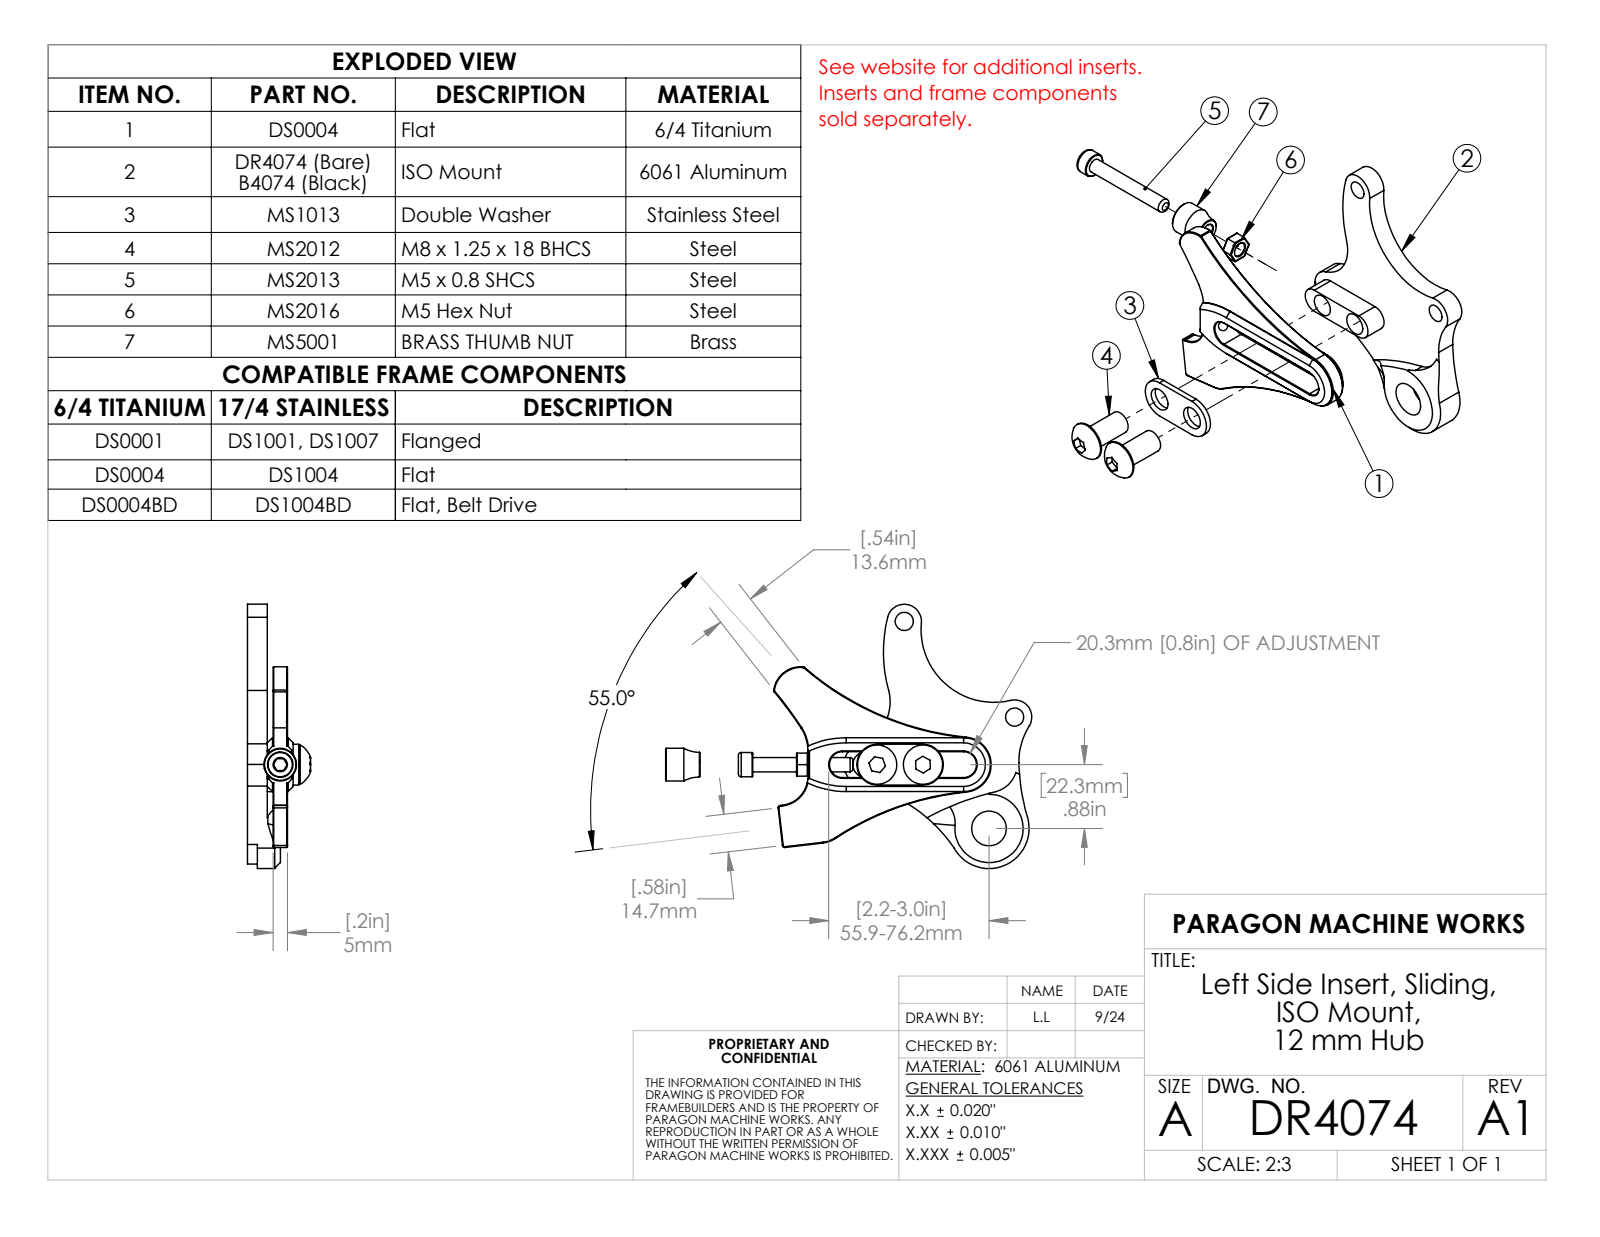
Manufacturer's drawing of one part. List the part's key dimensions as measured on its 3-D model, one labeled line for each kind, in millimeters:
Part name (STEP PRODUCT): MS2012; DR4074_Flat; MS2016; MS1013 (+4 more)
STEP written by: SolidWorks 2023 (AUTOMOTIVE_DESIGN)
Units: millimetres
Bodies: 8 solids, 257 faces (85 planar, 96 cylindrical, 76 other)
Overall size (bounding box): 175 × 134.9 × 92.3
Volume: 38 540 mm³ · Surface area: 20 460 mm²
Round holes (diameter × count): ⌀5 ×2, ⌀6.4 ×2, ⌀7.9 ×2, ⌀8.3 ×2, ⌀8.5 ×1, ⌀12.1 ×1
Round bosses / shafts (diameter × count): ⌀13.7 ×2, ⌀8 ×2, ⌀11.4 ×1
Partial cylindrical surfaces — rounded edges, fillets, slot ends (radius × count): R0.3 ×12, R0.8 ×4, R4.5 ×4, R6 ×2, R7.1 ×2, R10.2 ×2, R15.2 ×2, R32.3 ×2
Main face-to-face distances: 7, 5, 49.6, 42.6, 44.6, 37.6, 2, 7, 50.7, 43.7
Hole centre spacings: 16, 32.1, 35.6, 36, 39.9, 45, 50.4, 50.8
